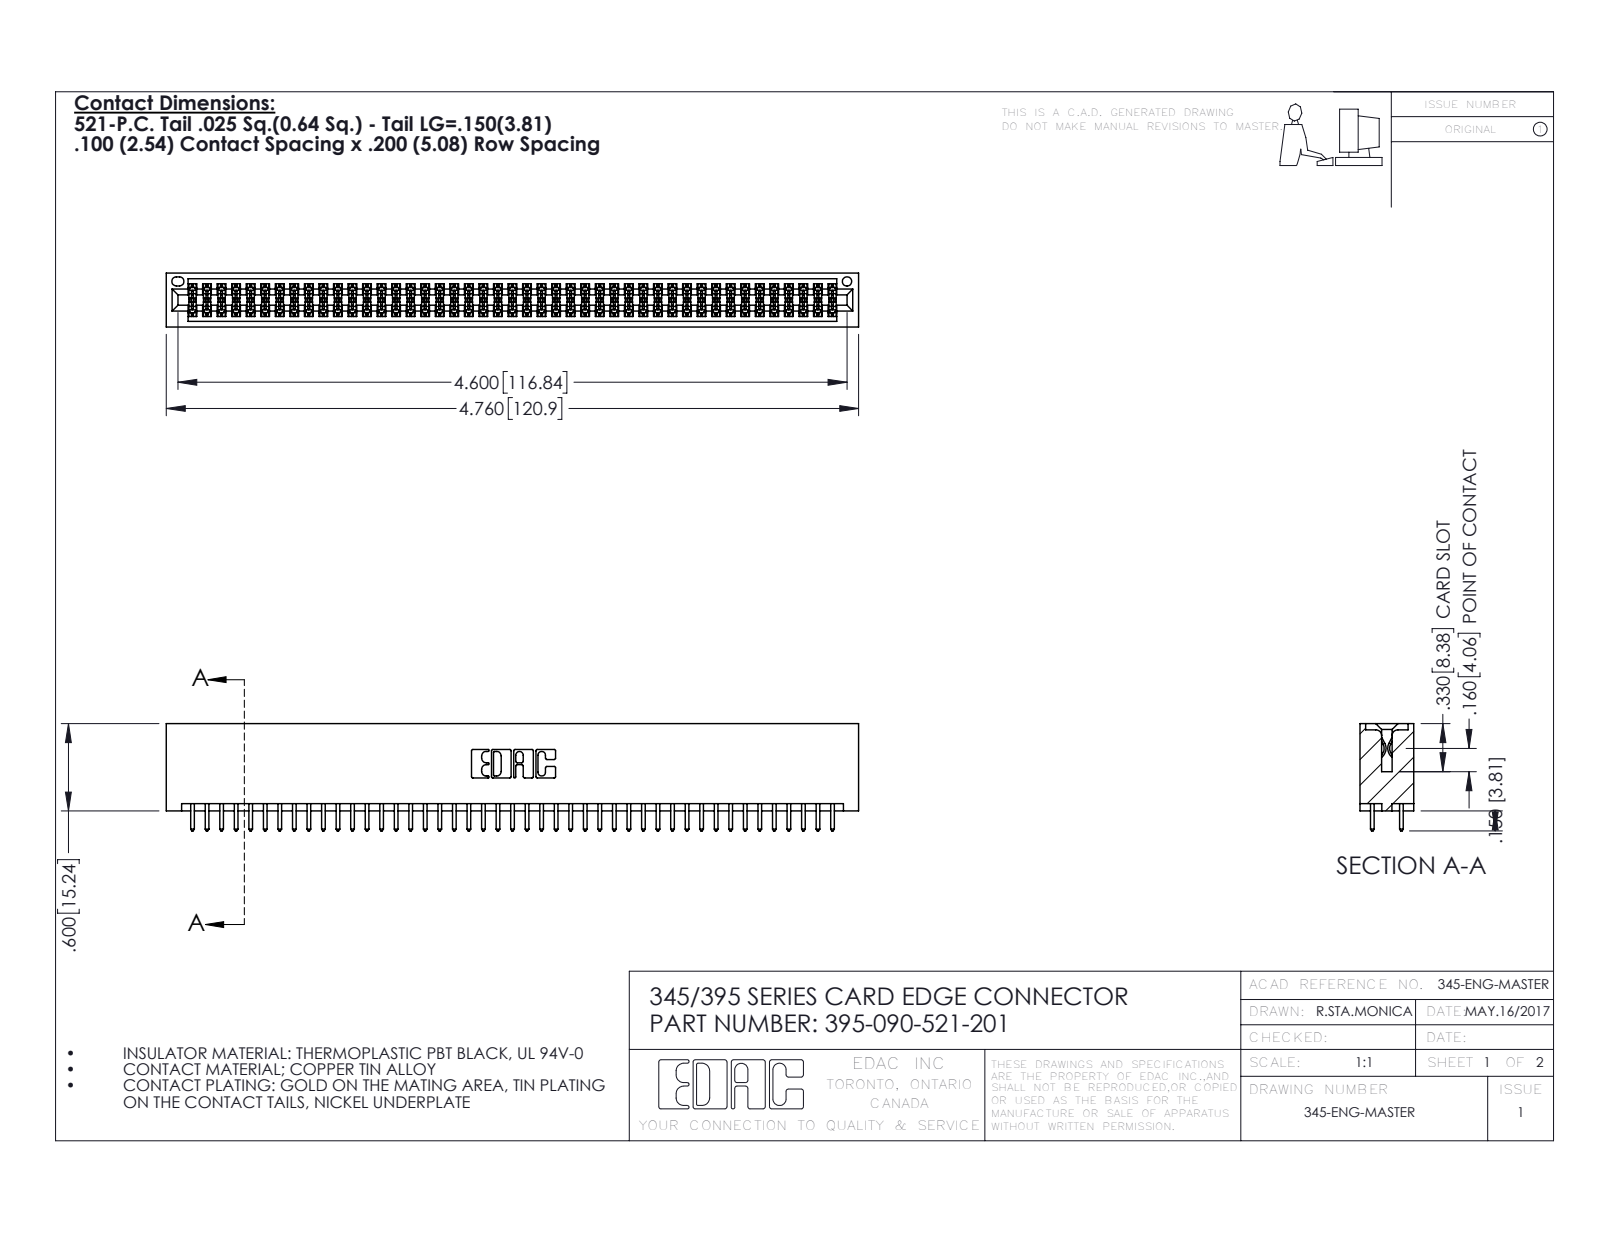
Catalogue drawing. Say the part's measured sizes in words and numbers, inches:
The part is named "345-292-001_345-293-121; 345 Part_No Mounting Lugs; 395-090-521-201". Its 3-D file was written by "SolidWorks 2016 (CONFIG_CONTROL_DESIGN)". It is 91 solids with 4618 faces: 3046 planar, 1572 cylindrical and 0 other. Overall it measures 4.76 by 0.737 by 0.37 inches. Its volume is 0.754 cubic inches and its surface area 28.49 square inches. Round holes: 1 of diameter 0.064. Partial cylindrical surfaces (rounded edges, fillets, slot ends): 135 of radius 0.006, 90 of radius 0.01, 22 of radius 0.01, 6 of radius 0.007, 6 of radius 0.031, 3 of radius 0.026, 2 of radius 0.014, 2 of radius 0.019. The main face-to-face distances are 0.298, 0.072, 0.2, 0.098, 0.272, 0.025, 0.37, 0.225, 0.175, 0.149.
